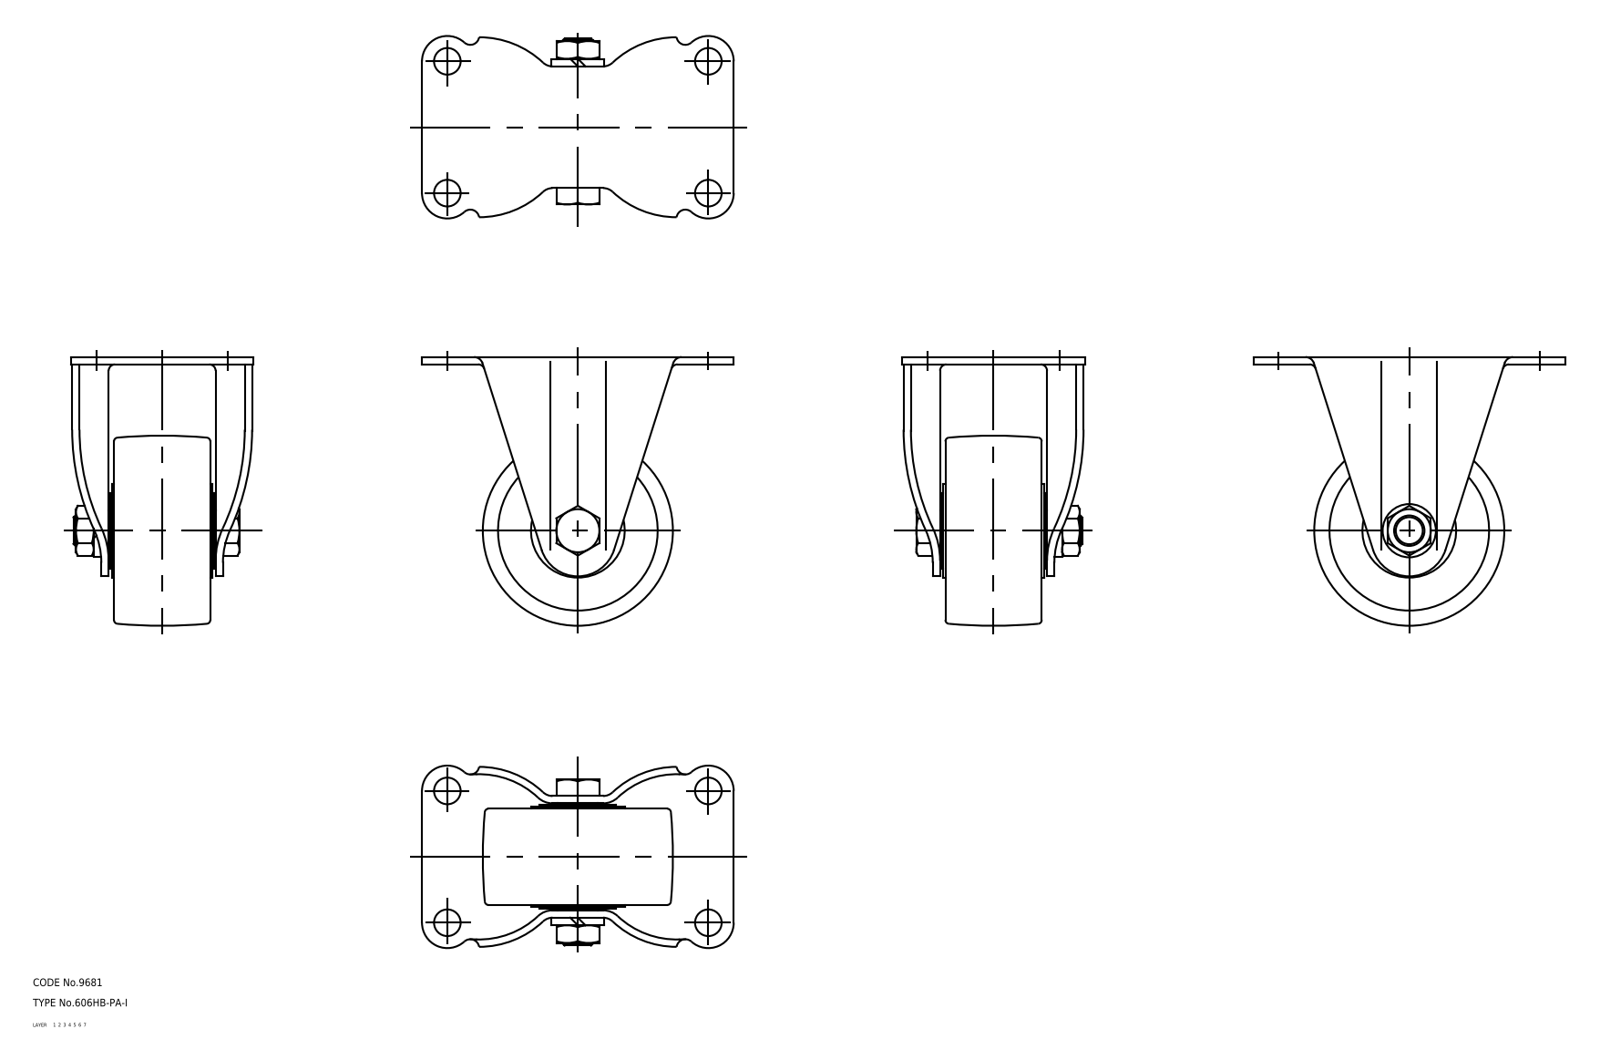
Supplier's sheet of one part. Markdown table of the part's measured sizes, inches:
| quantity | value |
| --- | --- |
| part name | 67119412; 67119425; 67119438 |
| STEP written by | CADfix (AUTOMOTIVE_DESIGN) |
| units | inches |
| bodies | 3 solids, 166 faces (0 planar, 0 cylindrical, 166 other) |
| overall size | 4.843 × 4.173 × 2.835 |
| volume | 13.28 in³ |
| surface area | 87.57 in² |
